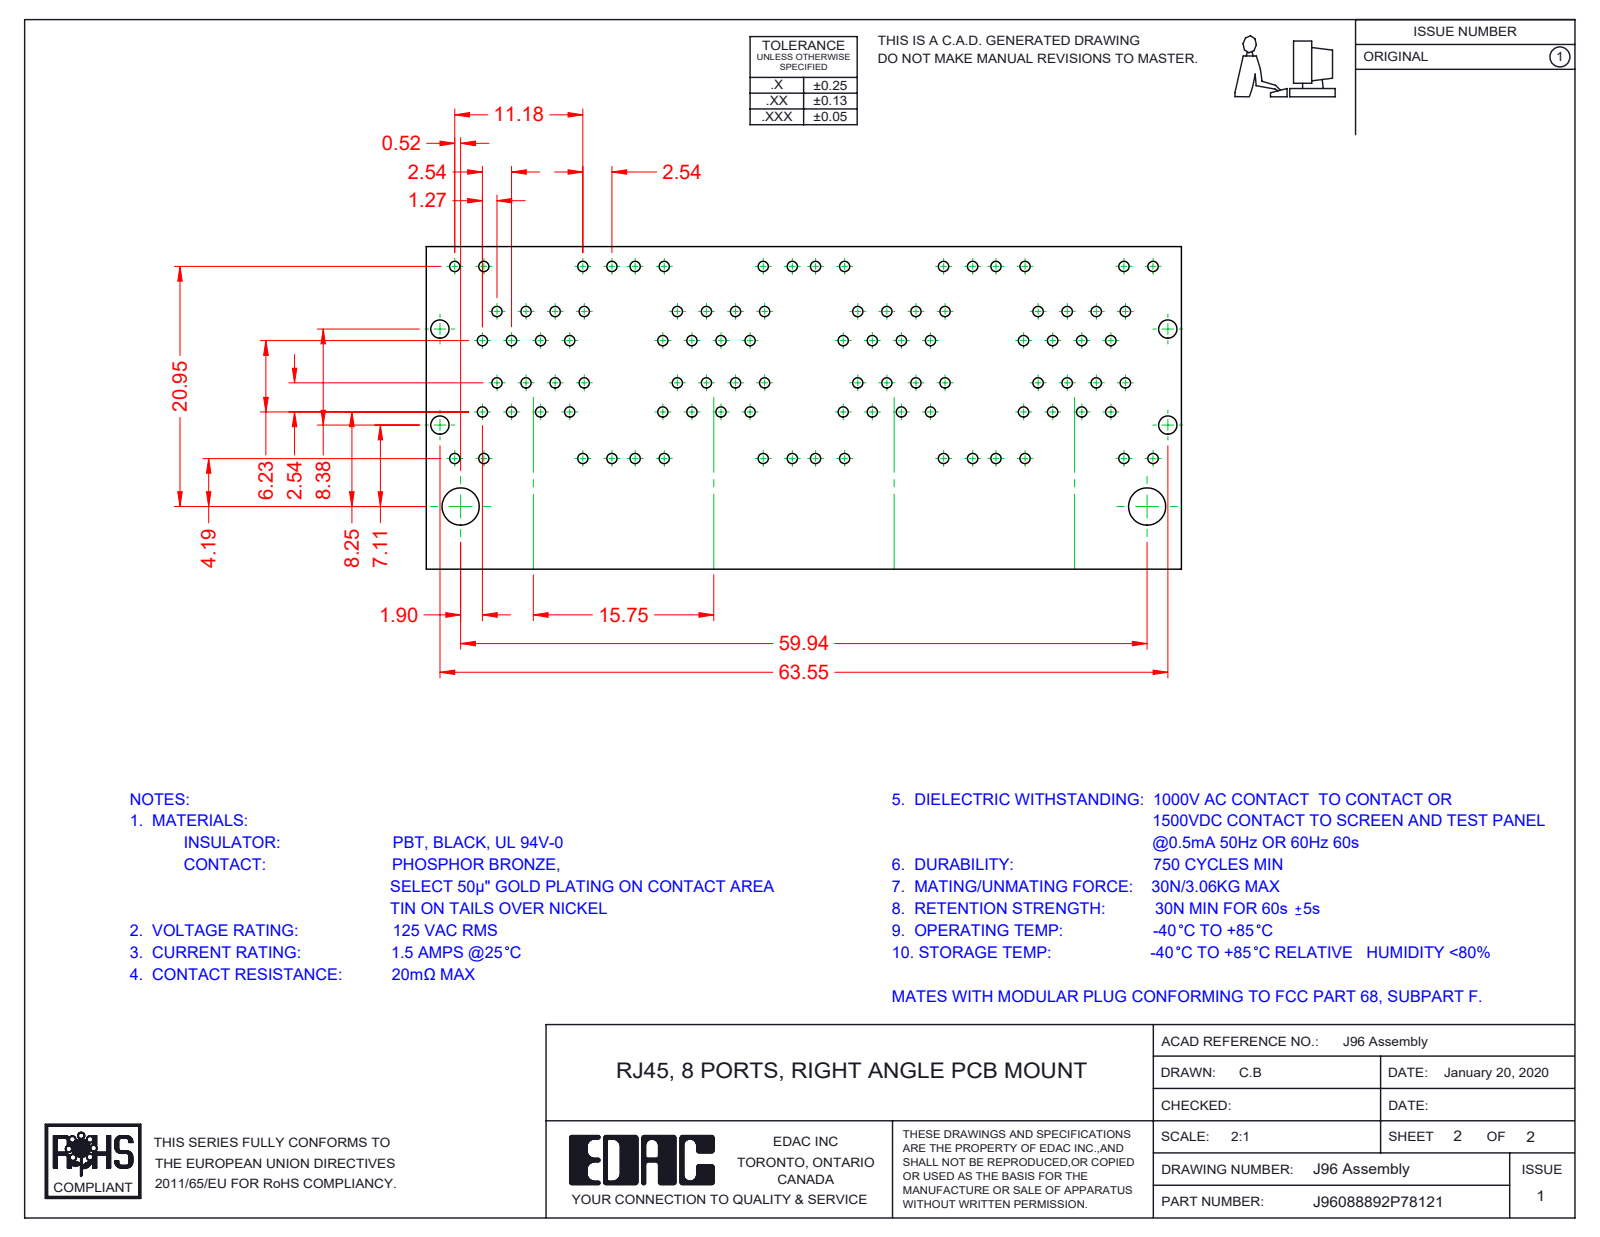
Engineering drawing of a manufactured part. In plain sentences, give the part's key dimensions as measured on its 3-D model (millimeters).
The part is named "96 Grounding_8 Ports; 96 Contact Lock Lower; 96 Back Plate_8 Ports; 96 LED RH Lower_8-Red-Yellow (+8 more)". Its 3-D file was written by "SolidWorks 2016 (CONFIG_CONTROL_DESIGN)". It is 96 solids with 7674 faces: 6069 planar, 1339 cylindrical and 266 other. Overall it measures 64.05 by 29.58 by 28.68 millimeters. Its volume is 24 160 cubic millimeters and its surface area 63 658 square millimeters. Round holes: 3 of diameter 1.7. Round bosses or shafts: 3 of diameter 1.68. Partial cylindrical surfaces (rounded edges, fillets, slot ends): 124 of radius 0.25, 73 of radius 0.35, 72 of radius 1, 49 of radius 0.5, 32 of radius 0.91, 21 of radius 0.2, 11 of radius 0.7, 8 of radius 0.22. The main face-to-face distances are 15.75, 0.35, 9.95, 1.17, 1.6, 0.54, 9.98, 10.18, 12.67, 3.37. The hole center spacings are 15.75, 31.5.
